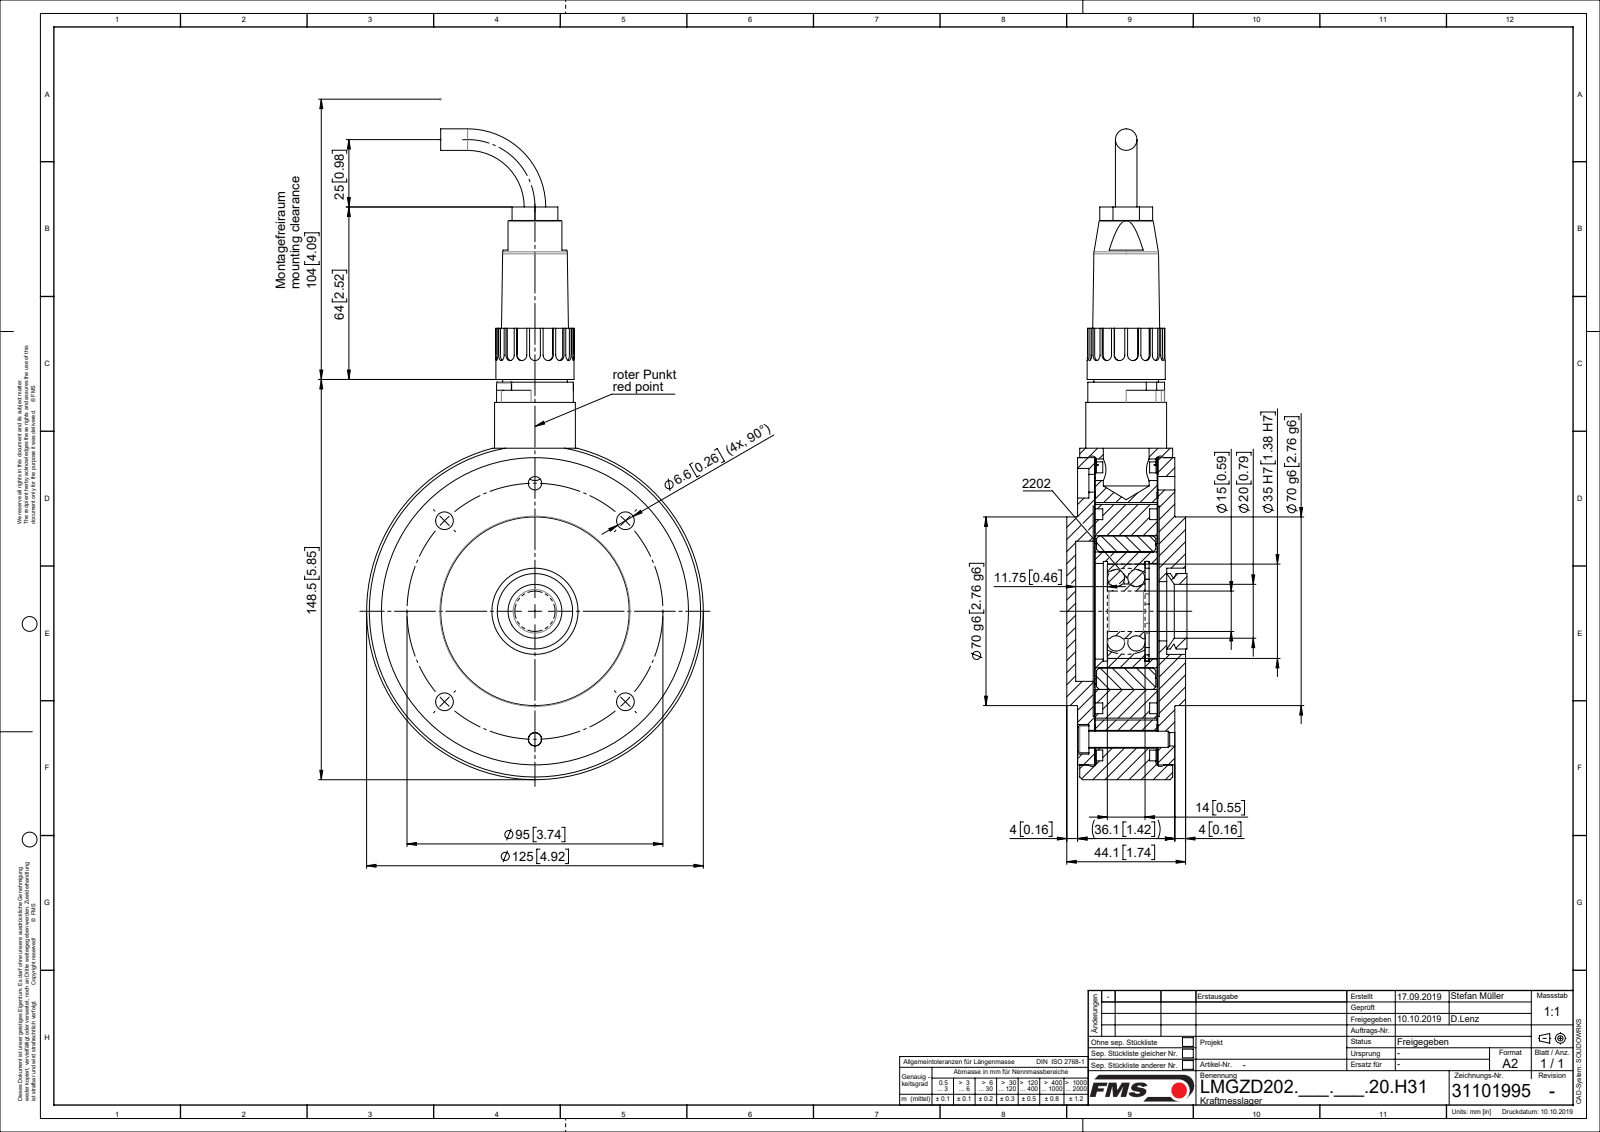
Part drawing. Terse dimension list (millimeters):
name: L48996; L4899503; TEIL1; L49009 (+8 more)
written by: Mechanical Desktop 2007 (CONFIG_CONTROL_DESIGN)
unit: mm
bodies: 17 solids, 403 faces (128 planar, 235 cylindrical, 40 other)
size: 241.5 × 125 × 44.1
volume: 474 991 mm³; area: 142 016 mm²
holes: 6× ⌀6.6, 4× ⌀2.49, 2× ⌀3, 2× ⌀3.6, 2× ⌀5, 2× ⌀11, 2× ⌀22, 1× ⌀10.5, 1× ⌀14, 1× ⌀15, 1× ⌀20, 1× ⌀23.6
bosses: 2× ⌀5.5, 1× ⌀125, 1× ⌀114, 1× ⌀103, 1× ⌀70, 1× ⌀29, 1× ⌀28.5, 1× ⌀28
rounds: 18× R2, 8× R5, 2× R3, 1× R40.5, 1× R47
face distances: 23.25, 23, 6.3, 6.55, 29.55, 29.8, 23.5, 5.8, 4, 30.3
hole spacings: 47.5, 16.26, 23, 36.36, 67.18, 87.77, 32.53, 95.01
